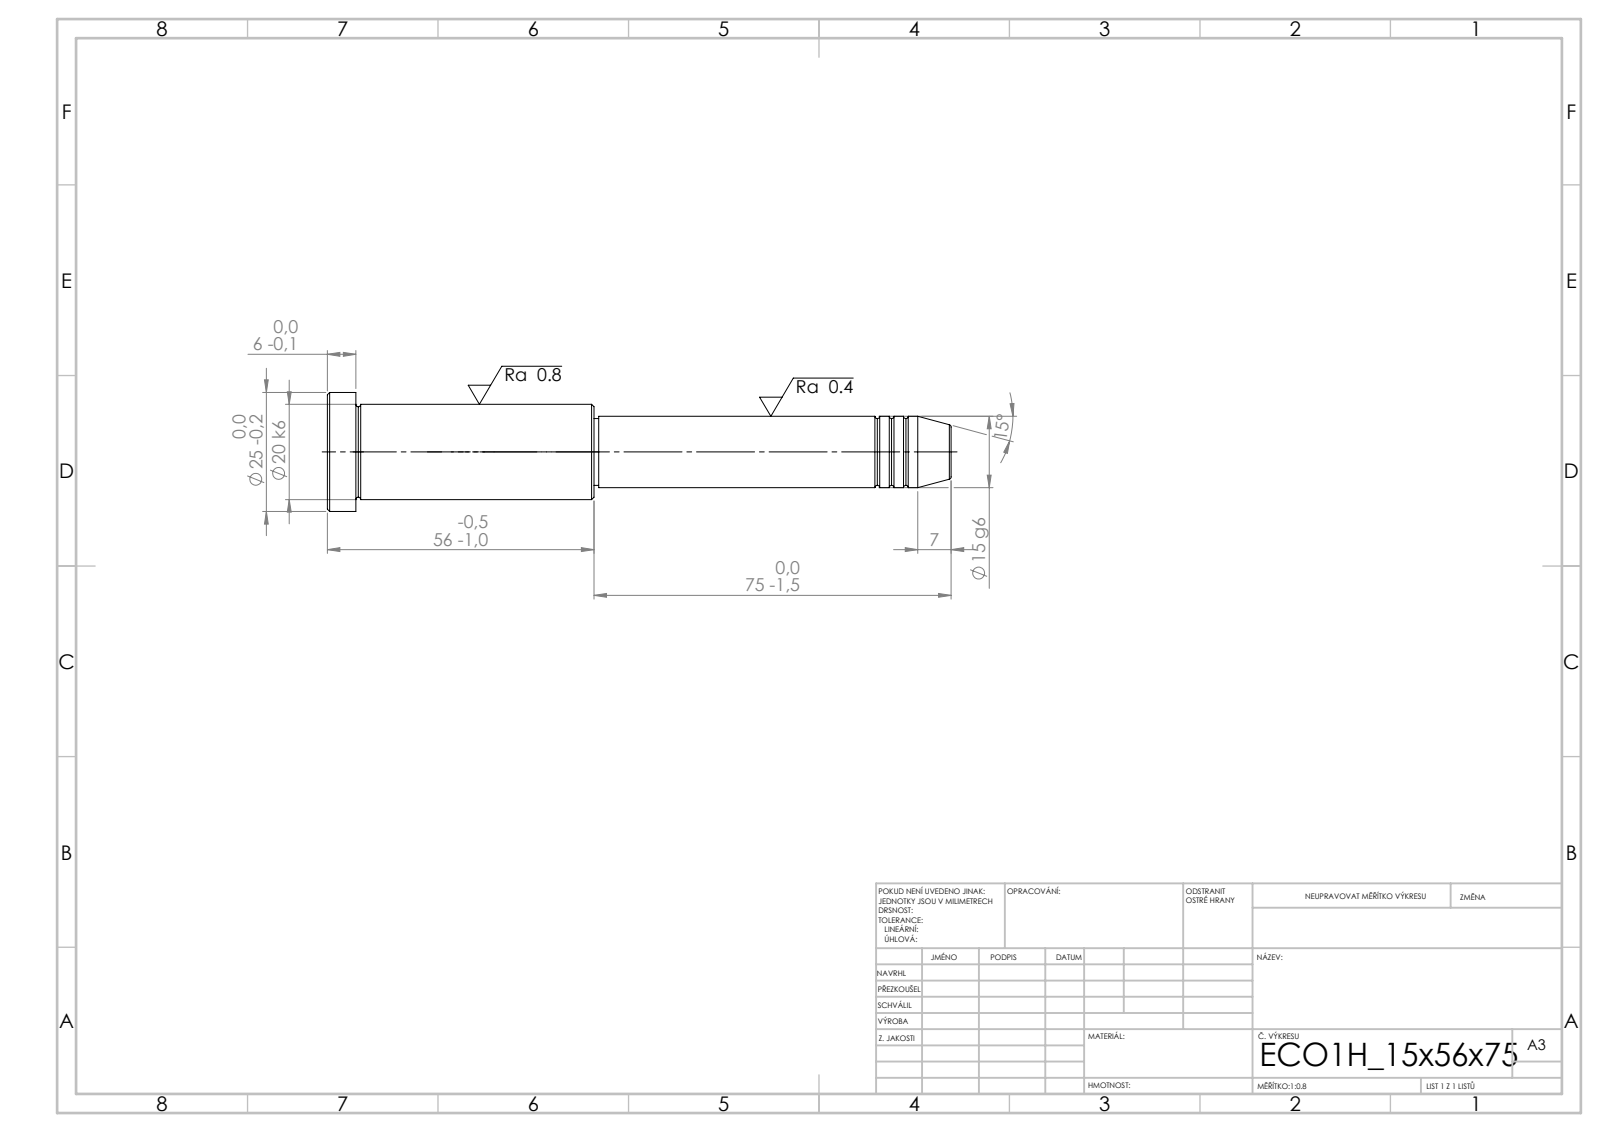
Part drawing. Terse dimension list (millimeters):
written by: SolidWorks 2019 (CONFIG_CONTROL_DESIGN)
unit: mm
bodies: 1 solid, 43 faces (5 planar, 14 cylindrical, 24 other)
size: 131 × 25 × 25
volume: 31 504 mm³; area: 8 121 mm²
bosses: 1× ⌀25, 1× ⌀20, 1× ⌀15, 1× ⌀14
face distances: 6, 50, 56, 75, 125, 131, 74, 1, 51, 57
